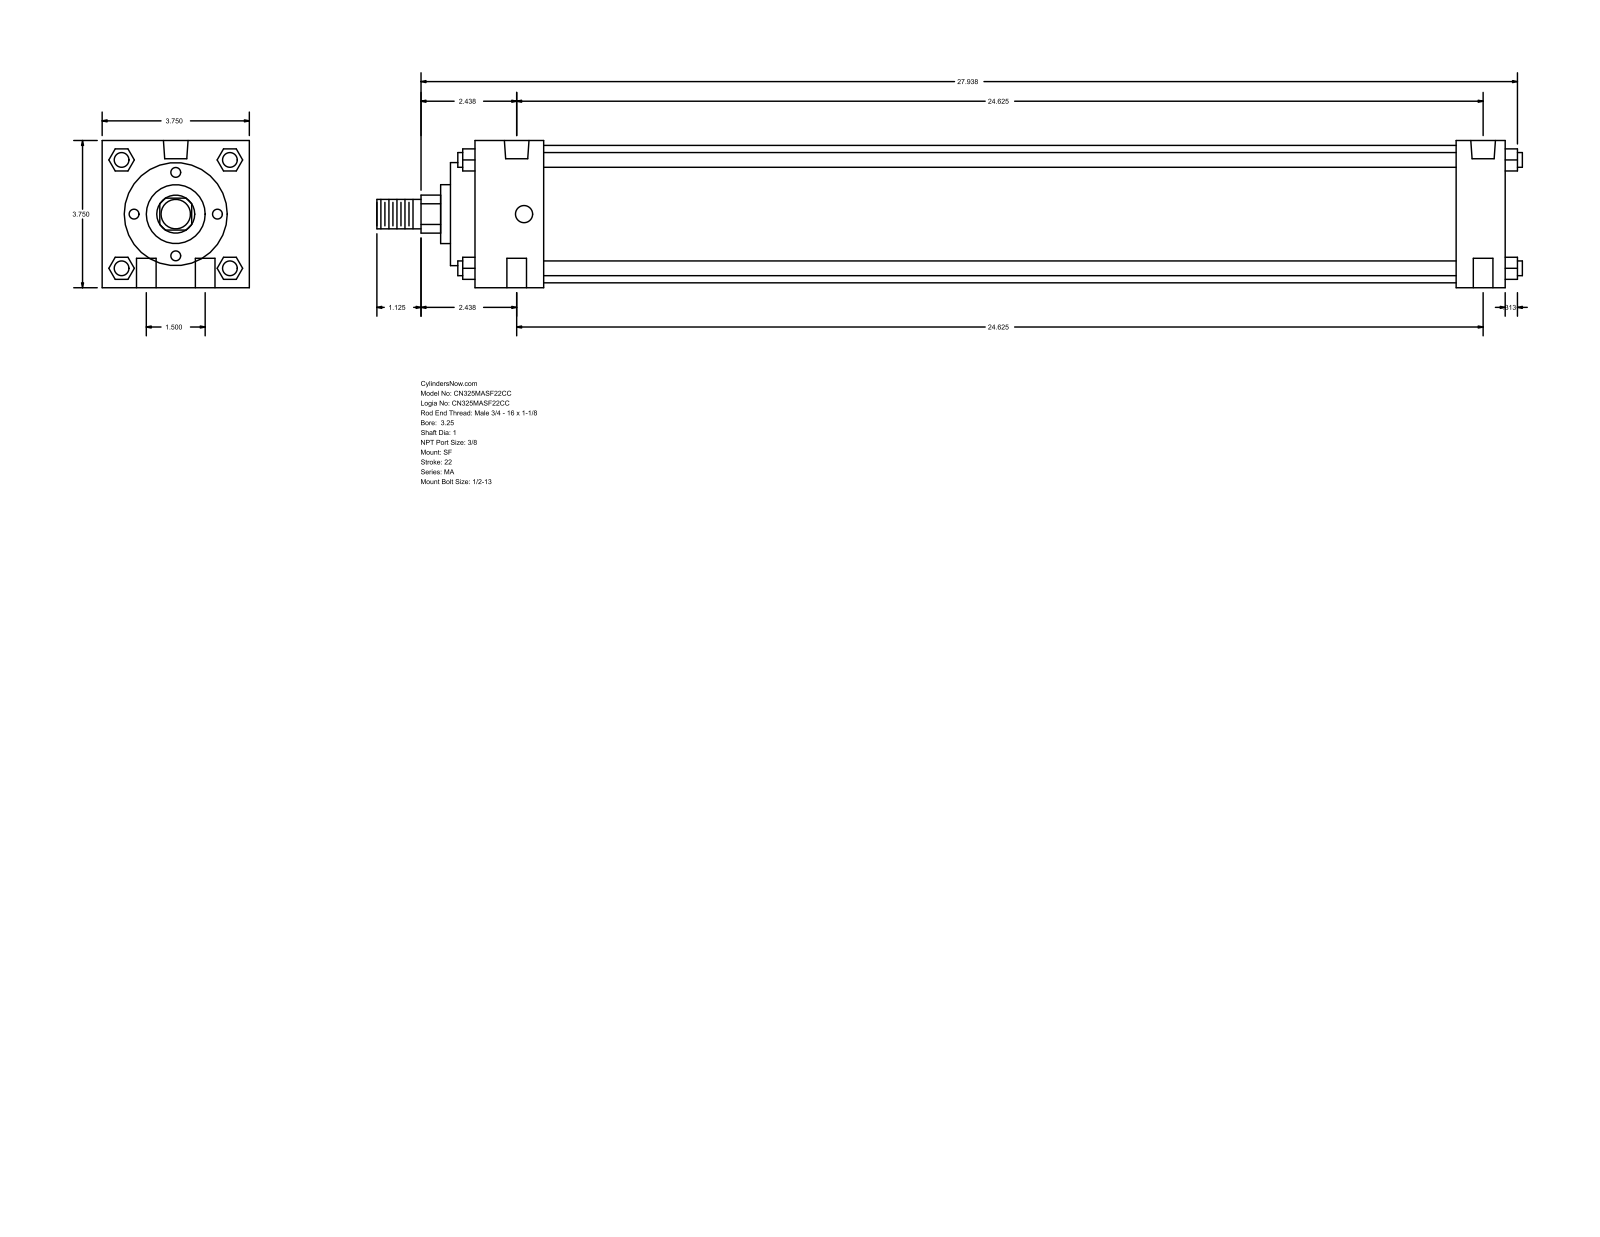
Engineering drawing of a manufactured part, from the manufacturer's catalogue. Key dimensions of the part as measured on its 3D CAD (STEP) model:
Part name (STEP PRODUCT): MA_SF__0325_1
STEP written by: GSSL Pune (CONFIG_CONTROL_DESIGN)
Units: millimetres
Bodies: 0 solids, 126 faces (95 planar, 31 cylindrical, 0 other)
Overall size (bounding box): 741.36 × 95.25 × 95.25
Round holes (diameter × count): ⌀12.7 ×4, ⌀11.11 ×2, ⌀15.93 ×2
Round bosses / shafts (diameter × count): ⌀9.53 ×4, ⌀88.9 ×1, ⌀66.67 ×1, ⌀38.1 ×1, ⌀25.4 ×1, ⌀19.05 ×1
Partial cylindrical surfaces — rounded edges, fillets, slot ends (radius × count): R12.29 ×1
Main face-to-face distances: 95.24, 666.75, 682.62, 635, 31.75, 44.46, 590.54, 622.29, 15.87, 60.33
Hole centre spacings: 19.05, 625.77, 625.48, 38.1, 626.64, 615.95
